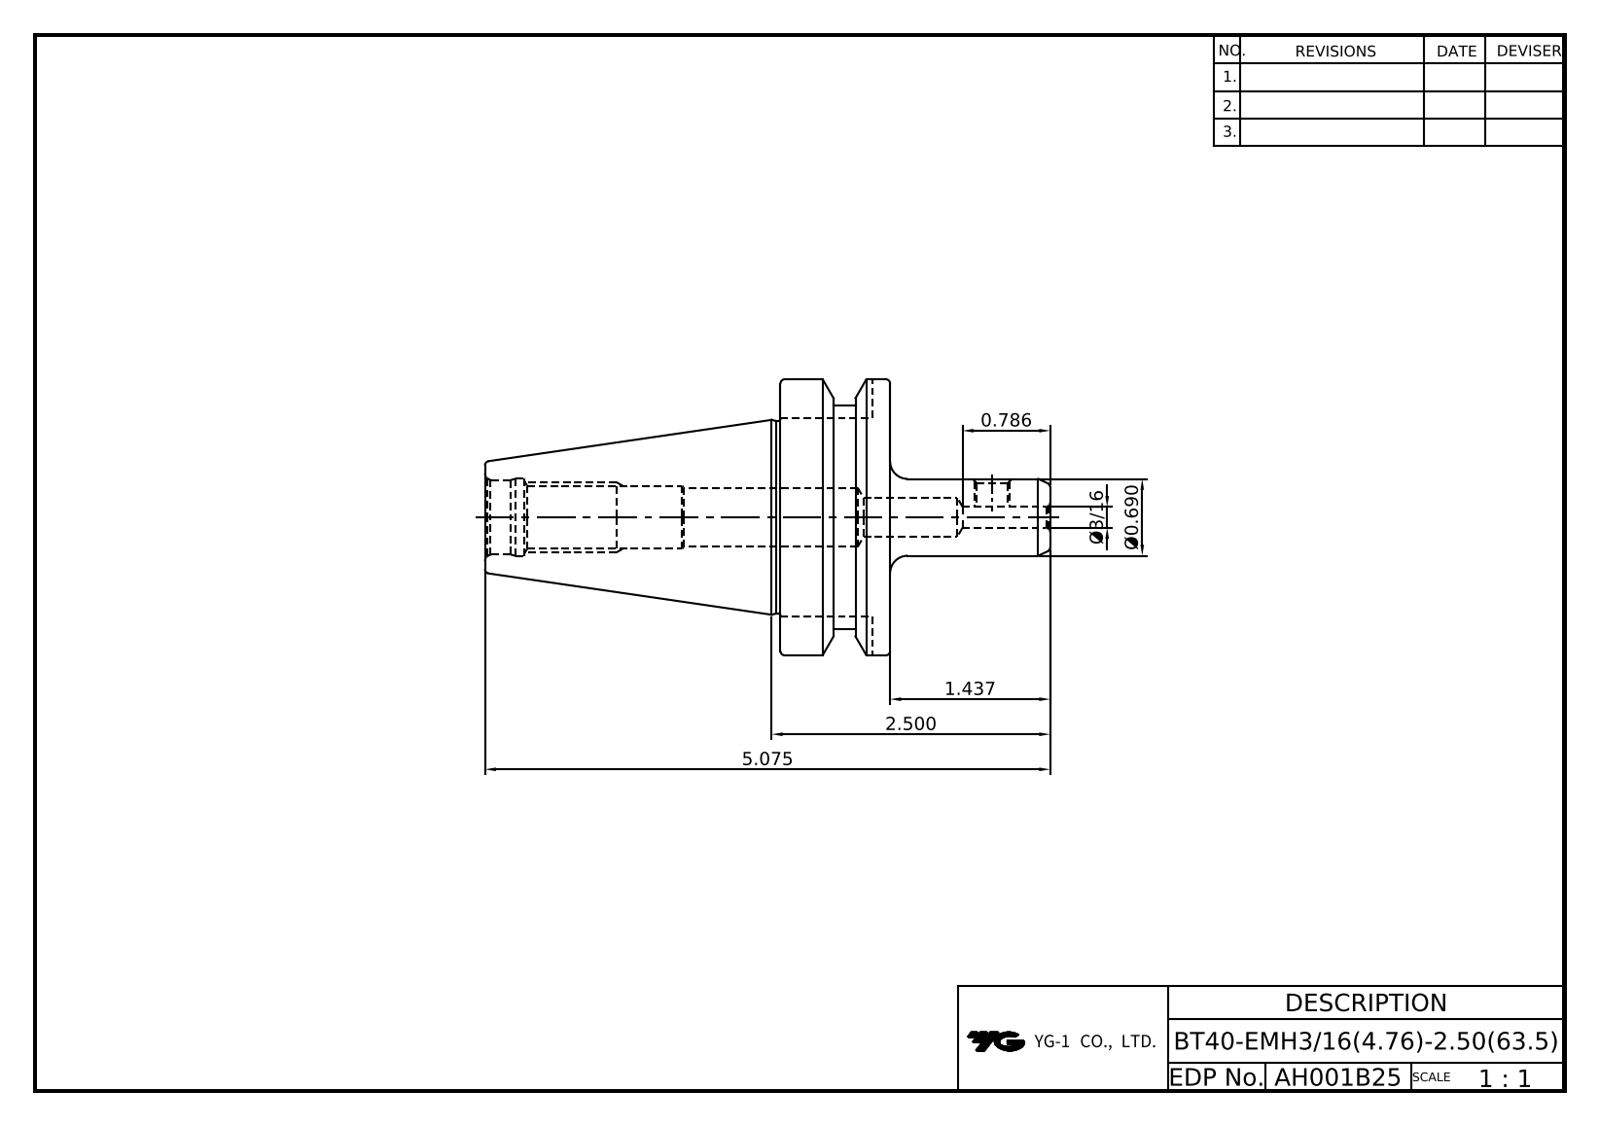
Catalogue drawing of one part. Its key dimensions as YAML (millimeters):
part_name: "LO-BT40-EMH3.175-63.5"
step_written_by: "Autodesk Inventor 2022 (AUTOMOTIVE_DESIGN)"
units: millimeters
bodies: {solids: 1, faces: 51, planar: 15, cylindrical: 16, other: 20}
overall_size: [128.9, 63, 63]
volume: 129846
surface_area: 24936
round_holes:
  - {diameter: 3.96, count: 1}
  - {diameter: 4.76, count: 1}
  - {diameter: 9, count: 1}
  - {diameter: 13.5, count: 1}
  - {diameter: 13.84, count: 1}
  - {diameter: 17, count: 1}
  - {diameter: 17.6, count: 1}
round_bosses_or_shafts:
  - {diameter: 63, count: 1}
  - {diameter: 52.6, count: 1}
  - {diameter: 44, count: 1}
  - {diameter: 17.53, count: 1}
partial_cylinders:
  - {radius: 8.05, count: 1}
face_to_face_distances: [25, 45.2, 16.1, 67.4, 92.4, 128.9, 61.5, 36.5, 84.5, 17.1]
